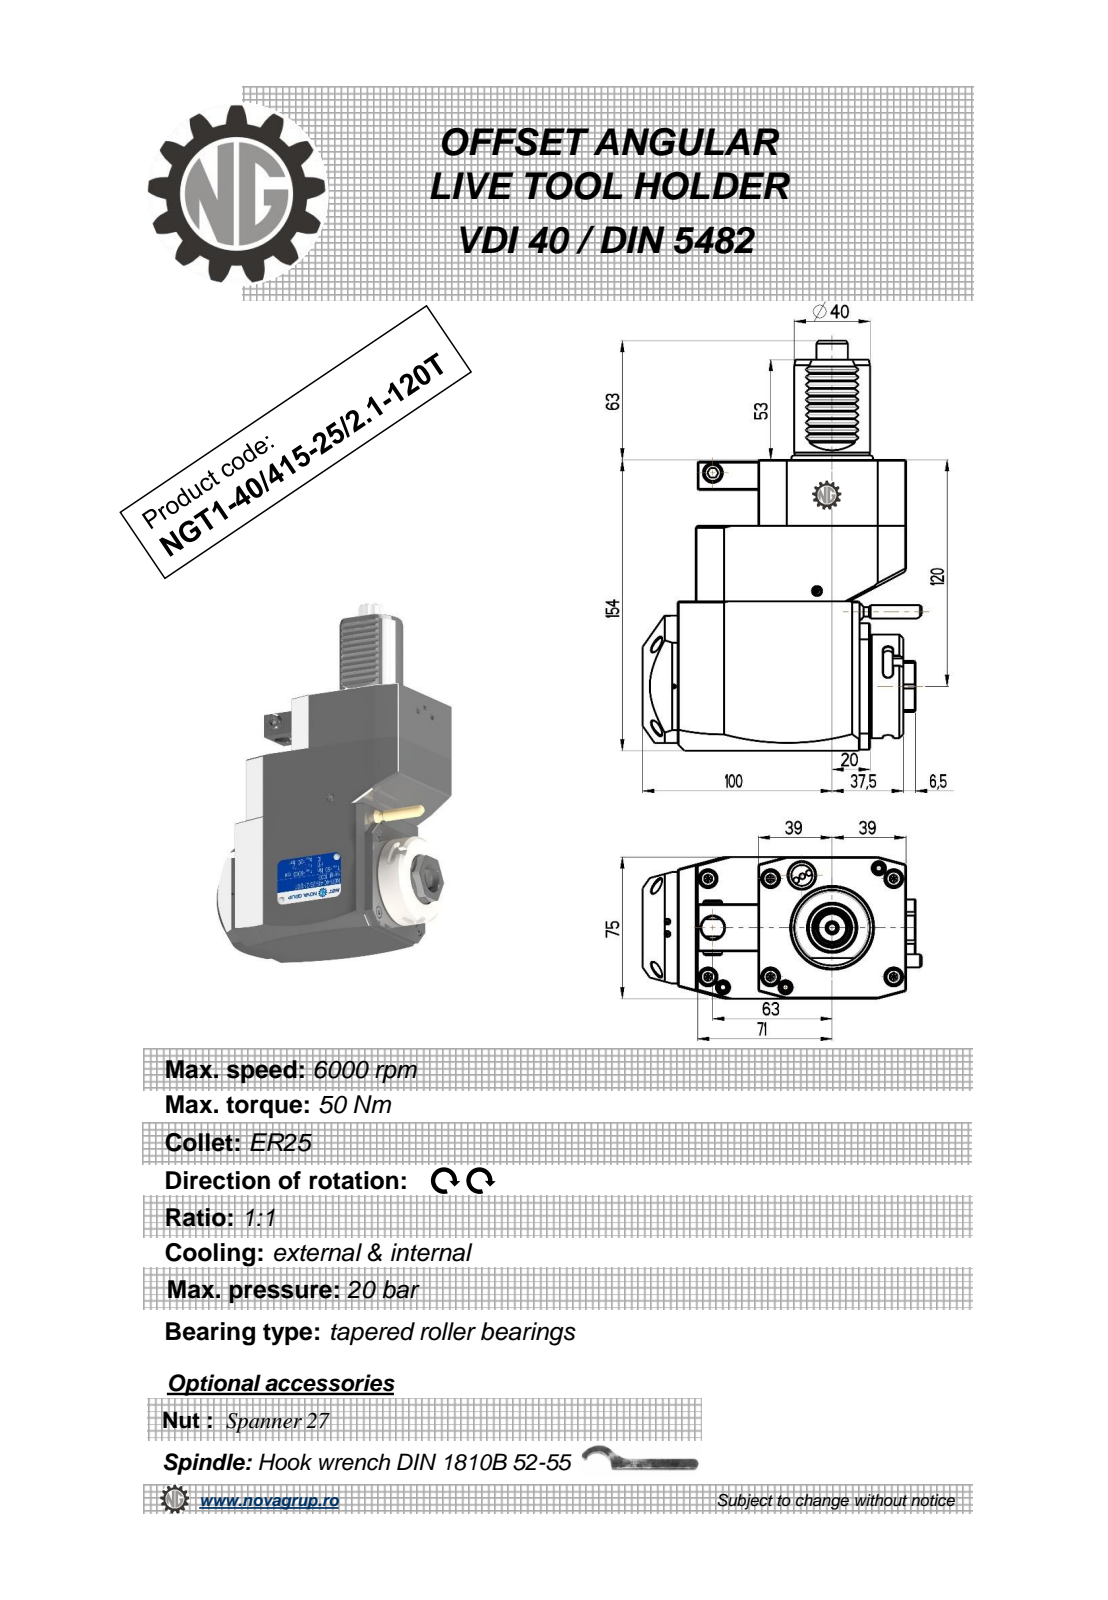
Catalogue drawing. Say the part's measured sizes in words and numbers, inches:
The part is named "NGT1_40_415_25_1_1_120T". Its 3-D file was written by "PRO/ENGINEER BY PARAMETRIC TECHNOLOGY CORPORATION, 2010280 (CONFIG_CONTROL_DESIGN)". It is 1 solid with 373 faces: 179 planar, 107 cylindrical and 87 other. Overall it measures 8.543 by 5.8 by 2.953 inches. Its volume is 76.71 cubic inches and its surface area 135.8 square inches. Round holes: 1 of diameter 0.098, 1 of diameter 0.118, 1 of diameter 0.165, 1 of diameter 0.209, 1 of diameter 0.374, 1 of diameter 0.472, 1 of diameter 0.709. Round bosses or shafts: 2 of diameter 0.353, 1 of diameter 2.165, 1 of diameter 1.89, 1 of diameter 1.575, 1 of diameter 0.394, 1 of diameter 0.276, 1 of diameter 0.197. Partial cylindrical surfaces (rounded edges, fillets, slot ends): 18 of radius 0.119, 10 of radius 0.012, 6 of radius 0.098, 2 of radius 7.087, 1 of radius 0.02, 1 of radius 0.167, 1 of radius 0.266, 1 of radius 0.325. The main face-to-face distances are 2.953, 6.063, 4.685, 0.748, 2.323, 4.37, 3.622, 1.378, 1.299, 0.689. The hole center spacings are 1.701, 2.48, 2.956, 4.429.
